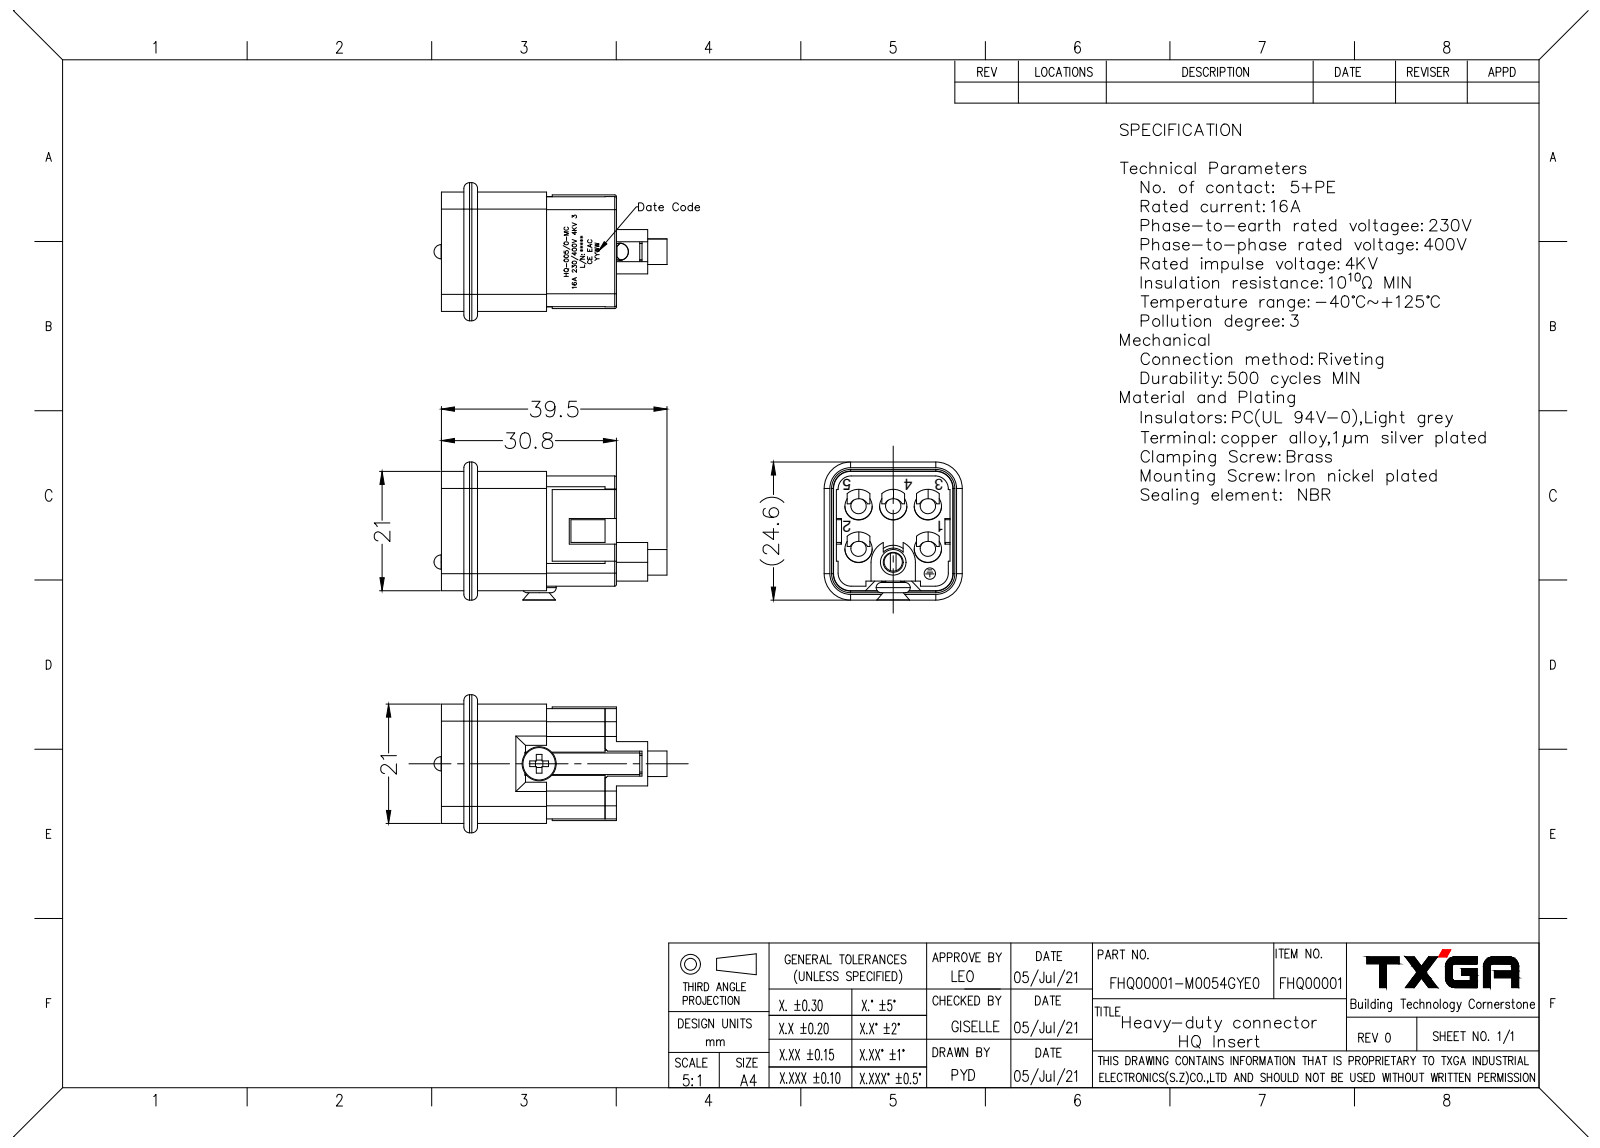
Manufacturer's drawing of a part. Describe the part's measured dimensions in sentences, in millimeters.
The part is named "FHQ00001-M0054GYE0 HQ-005&0-MC". Its 3-D file was written by "SolidWorks 2021 (CONFIG_CONTROL_DESIGN)". It is 1 solid with 470 faces: 246 planar, 142 cylindrical and 82 other. Overall it measures 41 by 24.3 by 24.3 millimeters. Its volume is 7 131 cubic millimeters and its surface area 8 819 square millimeters. Round holes: 6 of diameter 2.7, 1 of diameter 3, 1 of diameter 3.5, 1 of diameter 4. Round bosses or shafts: 1 of diameter 5.7, 1 of diameter 4.5, 1 of diameter 3.2, 1 of diameter 2.9, 1 of diameter 2.6, 1 of diameter 2.5. Partial cylindrical surfaces (rounded edges, fillets, slot ends): 30 of radius 0.3, 12 of radius 1, 11 of radius 2.4, 10 of radius 3, 8 of radius 0.5, 6 of radius 2.3, 5 of radius 1.73, 5 of radius 4.25. The main face-to-face distances are 19.6, 1.4, 21, 0.8, 0.9, 19.3, 1.7, 18.2, 18.5, 20.2. The hole center spacings are 6.1, 6.54, 6.56, 7.5, 9.67, 11.59, 11.63, 12.2.
